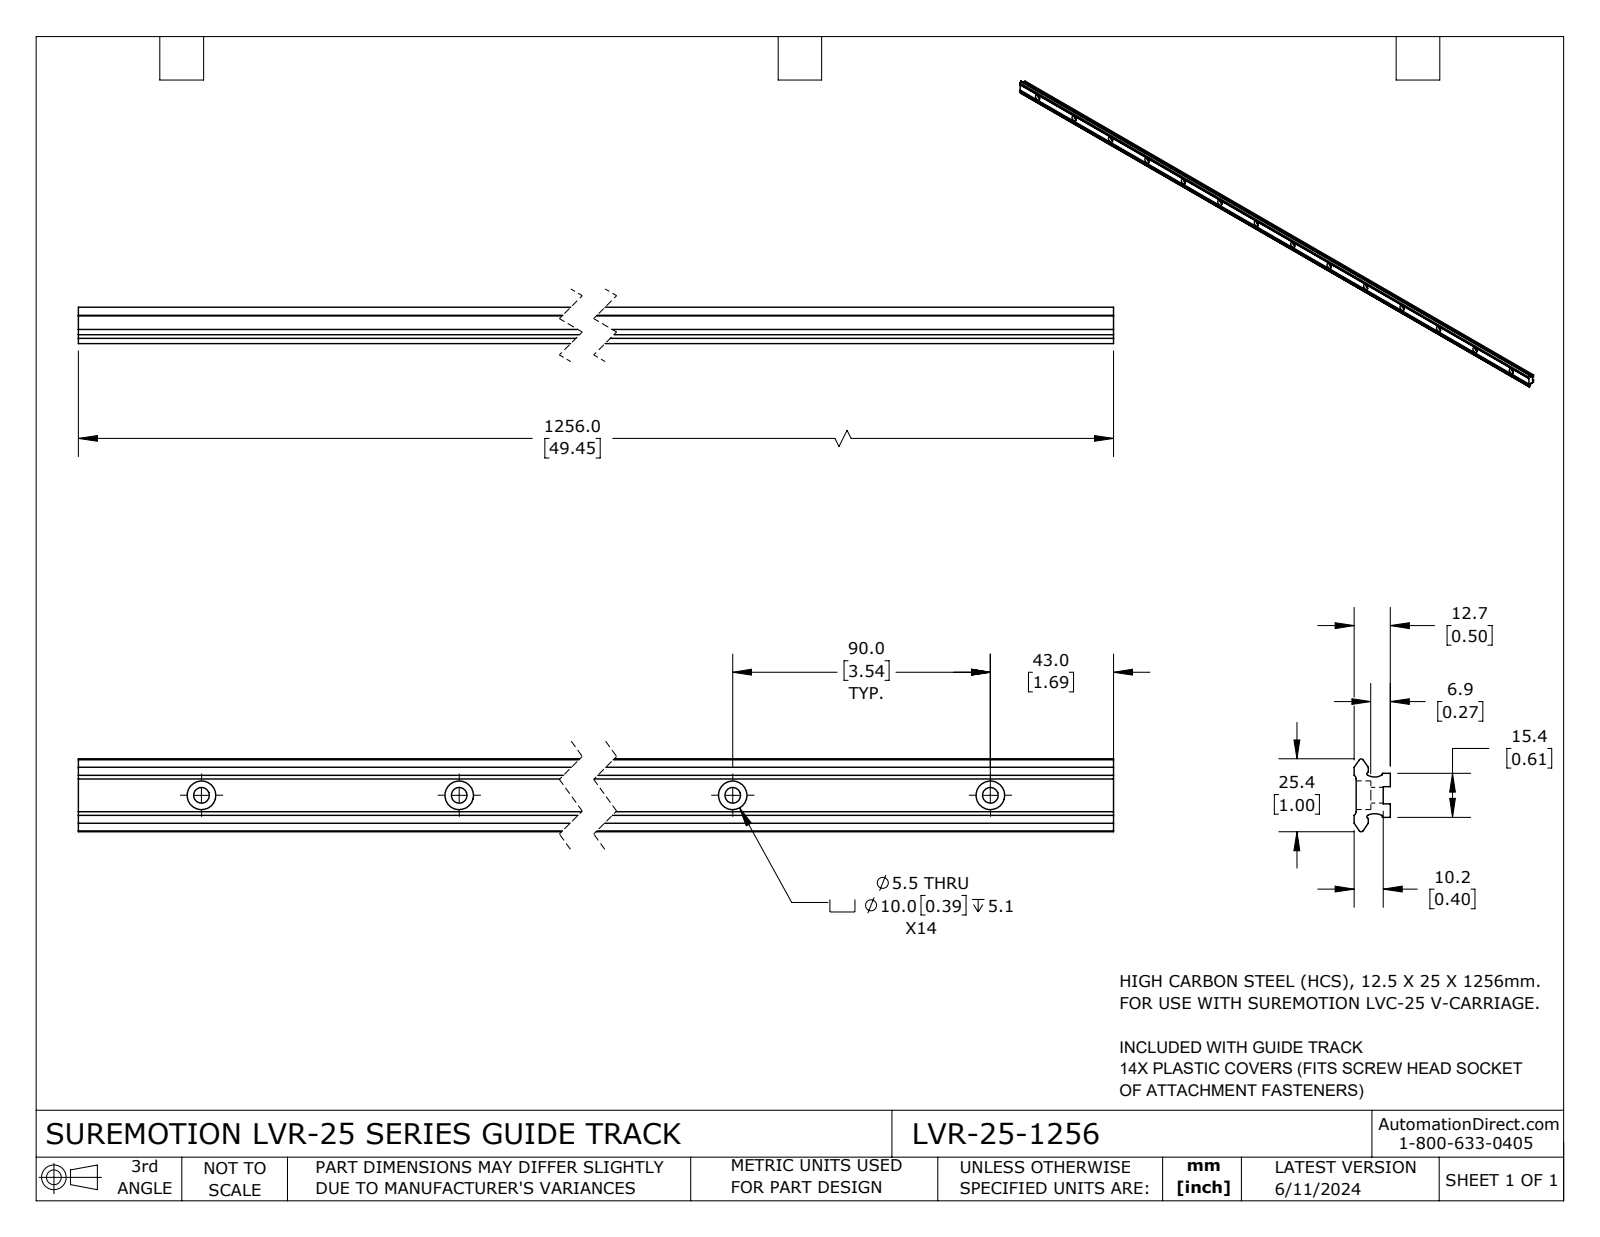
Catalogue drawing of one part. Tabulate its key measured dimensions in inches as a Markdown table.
| quantity | value |
| --- | --- |
| part name | LVR-25-1256 |
| STEP written by | SolidWorks 2023 (CONFIG_CONTROL_DESIGN) |
| units | inches |
| bodies | 1 solid, 100 faces (32 planar, 68 cylindrical, 0 other) |
| overall size | 49.449 × 1.002 × 0.498 |
| volume | 14.61 in³ |
| surface area | 160.2 in² |
| round holes (diameter × count) | 0.217 × 14, 0.394 × 14 |
| partial cylindrical surfaces (radius × count) | 0.022 × 4, 0.03 × 2, 0.059 × 2, 0.206 × 2 |
| main face-to-face distances | 0.471, 0.6, 0.098, 0.372, 0.498, 0.4, 0.028, 0.185, 0.421, 0.304 |
| hole center spacings | 3.543, 7.087, 10.63, 14.173, 17.717, 21.26, 24.803, 28.346 |
